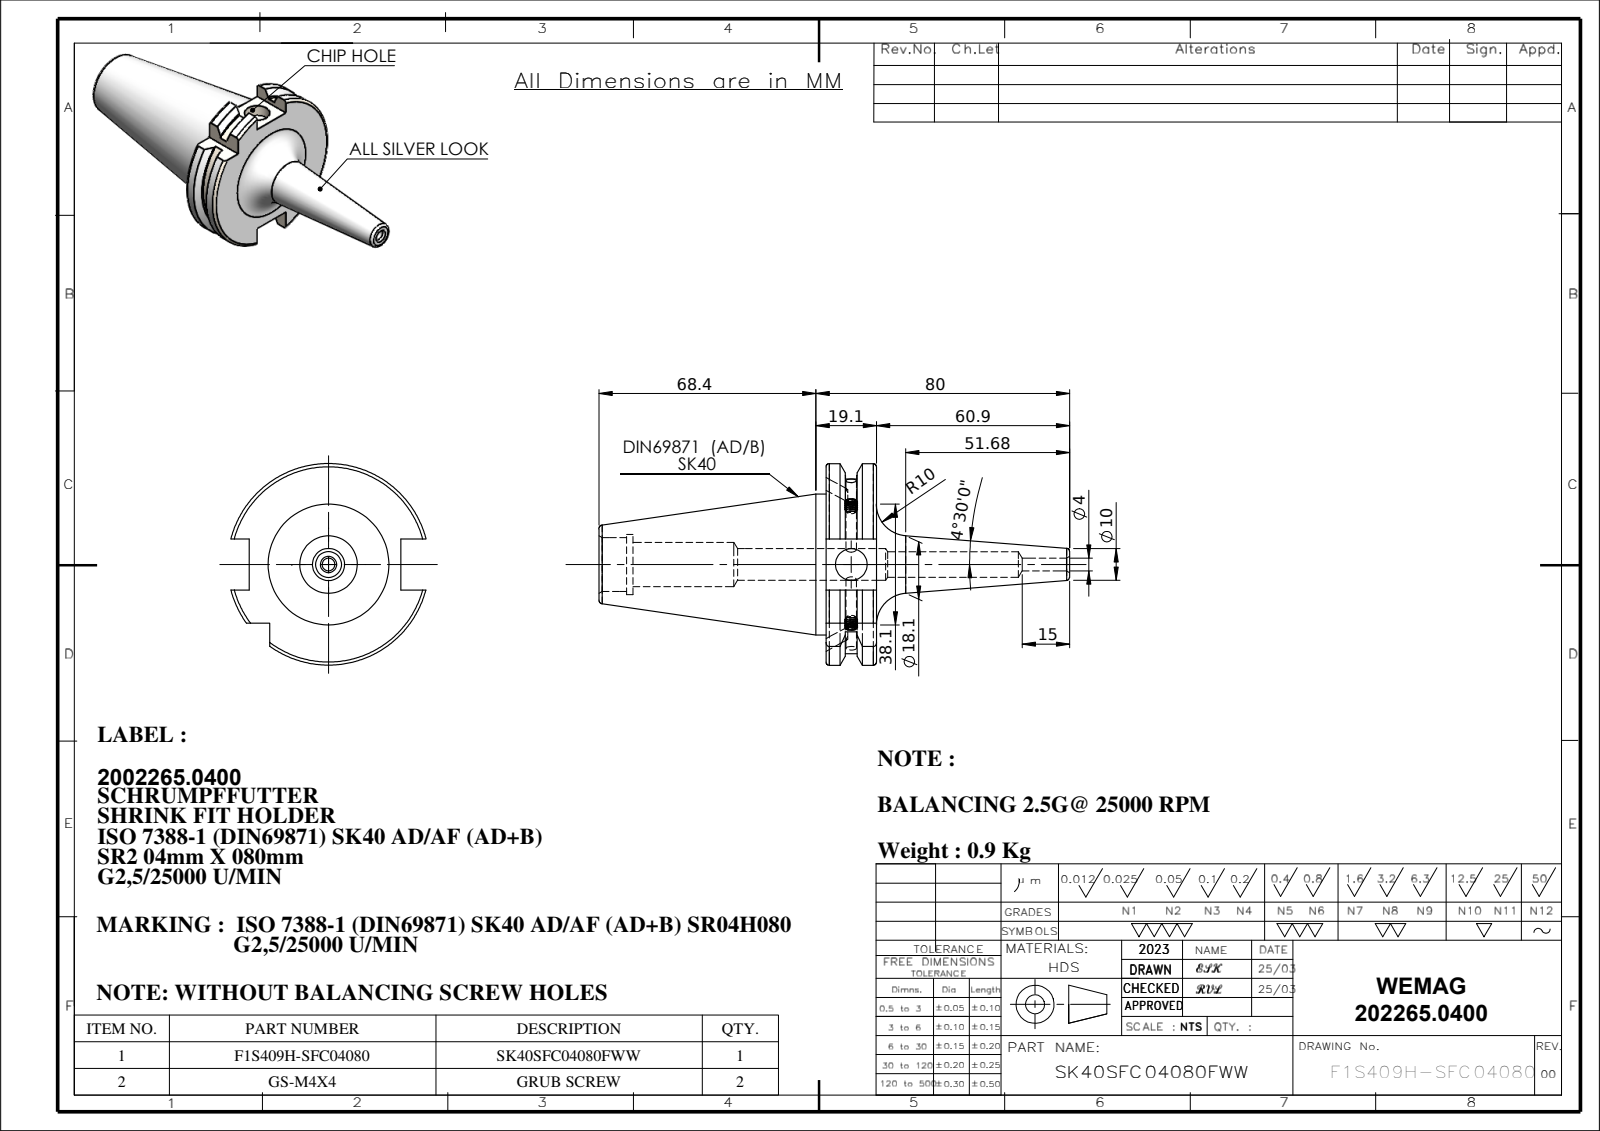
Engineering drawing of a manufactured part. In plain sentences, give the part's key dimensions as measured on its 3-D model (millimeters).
The part is named "91406-SR214080; SK40SFC04080FWW; GS-M4X4_DIN 913 - M4 x 4-N". Its 3-D file was written by "SolidWorks 2018 (CONFIG_CONTROL_DESIGN)". It is 3 solids with 194 faces: 46 planar, 52 cylindrical and 96 other. Overall it measures 148.4 by 63.55 by 61.48 millimeters. Its volume is 111 259 cubic millimeters and its surface area 24 937 square millimeters. Round holes: 2 of diameter 10, 1 of diameter 3.3, 1 of diameter 3.99, 1 of diameter 8, 1 of diameter 14, 1 of diameter 17, 1 of diameter 19. Round bosses or shafts: 2 of diameter 4, 1 of diameter 44.45. Partial cylindrical surfaces (rounded edges, fillets, slot ends): 1 of radius 28.12, 1 of radius 31.77. The main face-to-face distances are 15.9, 16.1, 47.8, 60.9, 76.8, 71.6, 87.5, 10.7, 77.63, 66.93.
